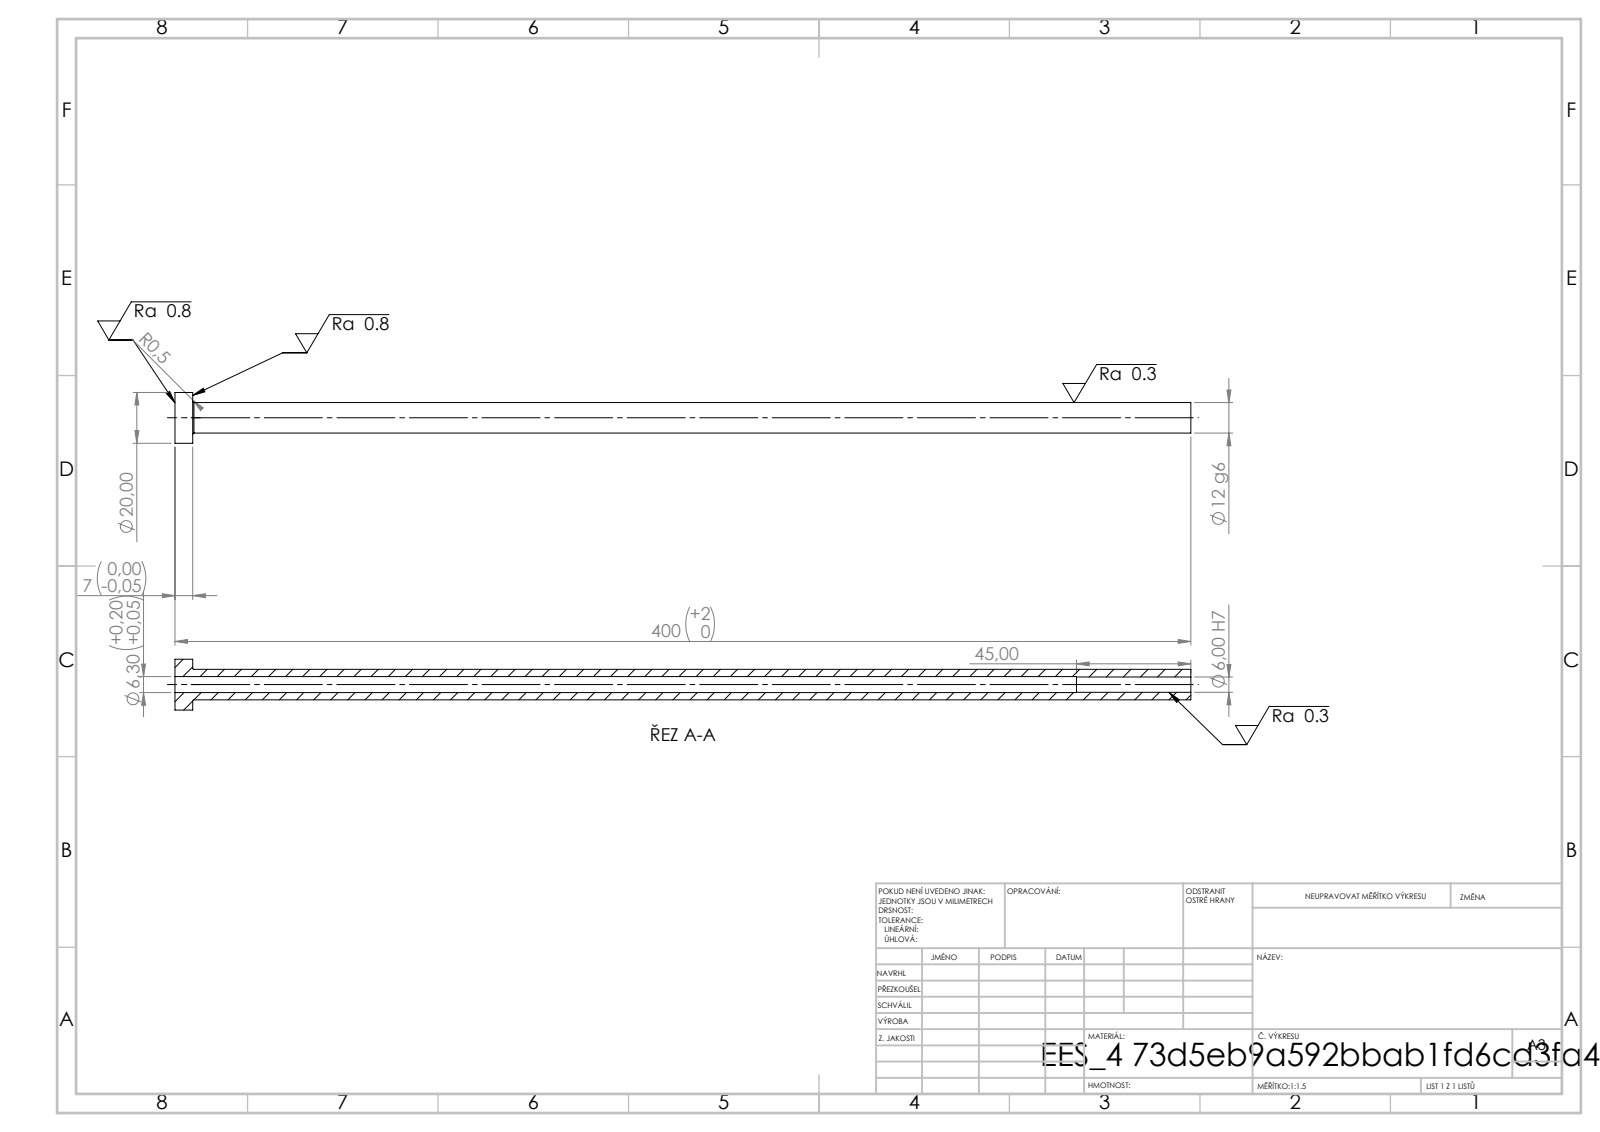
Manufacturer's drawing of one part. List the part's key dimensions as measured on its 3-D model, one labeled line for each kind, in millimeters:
STEP written by: SolidWorks 2019 (CONFIG_CONTROL_DESIGN)
Units: millimetres
Bodies: 1 solid, 14 faces (4 planar, 8 cylindrical, 2 other)
Overall size (bounding box): 400 × 20 × 20
Volume: 34 310 mm³ · Surface area: 23 694 mm²
Round holes (diameter × count): ⌀6 ×1, ⌀6.3 ×1
Round bosses / shafts (diameter × count): ⌀20 ×1, ⌀12 ×1
Main face-to-face distances: 7, 400, 393, 355, 348, 45
